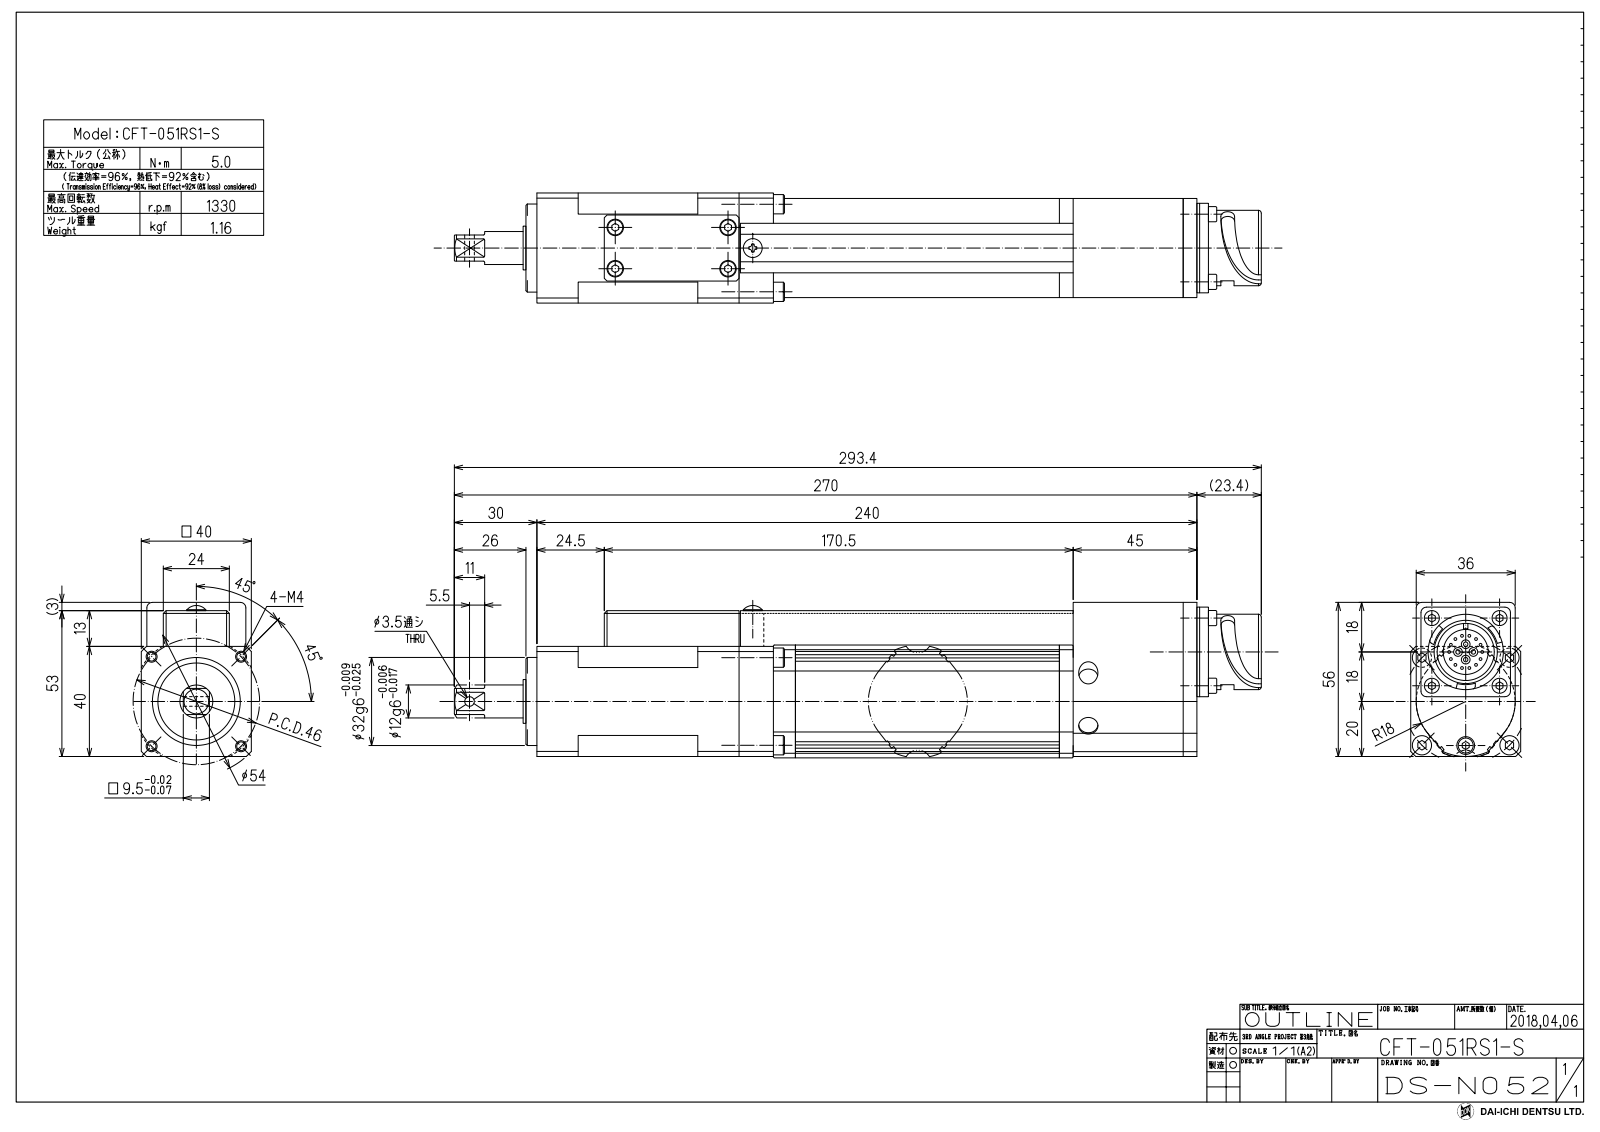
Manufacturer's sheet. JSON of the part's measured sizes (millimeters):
{"part_name": "CFT-051RS1-S", "step_written_by": "SolidWorks 2017 (AUTOMOTIVE_DESIGN)", "units": "millimeters", "bodies": {"solids": 20, "faces": 411, "planar": 243, "cylindrical": 116, "other": 52}, "overall_size": [293.4, 56.06, 40], "volume_mm3": 373421, "surface_area_mm2": 78562, "round_holes": [[3.3, 4], [6, 4], [3.5, 1], [20.8, 1]], "round_bosses_or_shafts": [[5.5, 8], [7, 4], [32, 1], [27.4, 1], [24.4, 1], [15.9, 1], [12, 1], [6.9, 1]], "partial_cylinders_radius": [[2, 8], [0.5, 4], [4, 2], [5, 2], [18, 1], [20, 1], [20.5, 1], [23.5, 1]], "face_to_face_distances": [40, 5, 2, 45, 11, 13, 27, 16, 8, 6], "hole_center_spacings": [32.52, 15, 16.35, 37.92, 41, 43.66, 45.99]}
